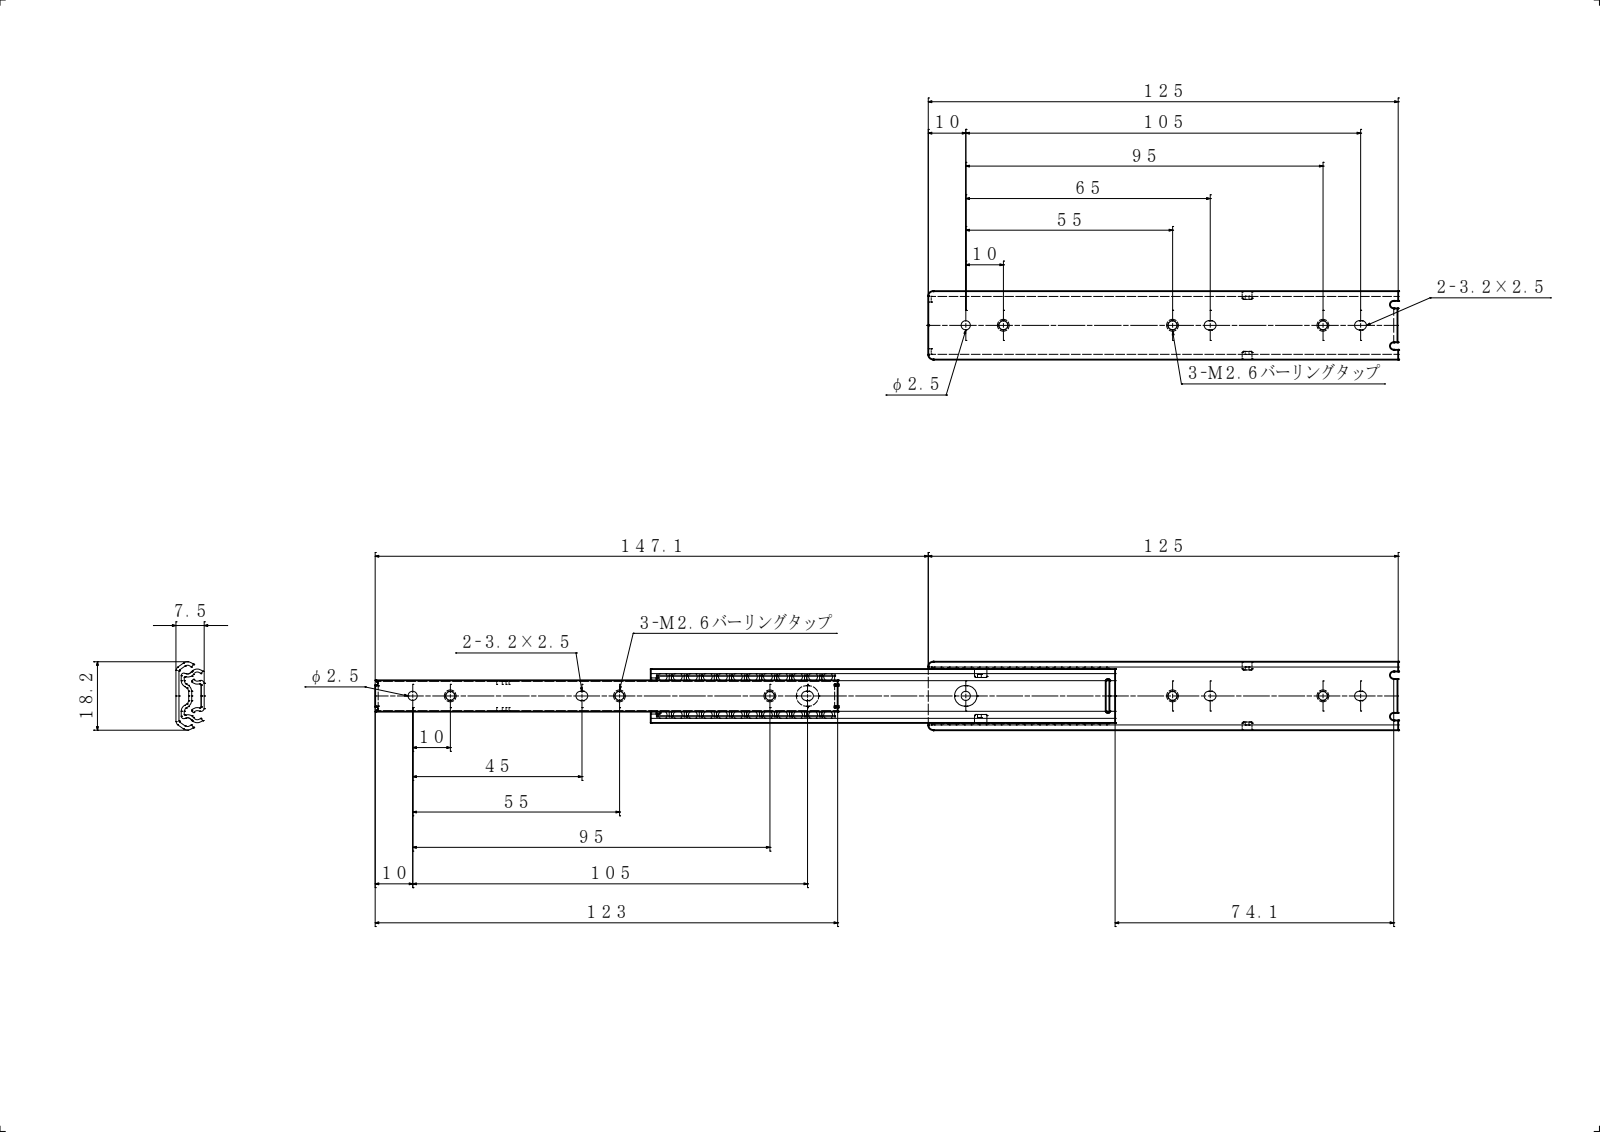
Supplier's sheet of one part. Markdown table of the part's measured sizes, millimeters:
| quantity | value |
| --- | --- |
| part name | UC180-125; UC180-125 IM; UC180-125 OM; UC180-125 CM |
| STEP written by | SolidWorks 2019 (CONFIG_CONTROL_DESIGN) |
| units | millimeters |
| bodies | 5 solids, 486 faces (198 planar, 234 cylindrical, 54 other) |
| overall size | 272.1 × 18.3 × 7.5 |
| volume | 6 056 mm³ |
| surface area | 16 079 mm² |
| round holes (diameter × count) | 2.2 × 3, 2.4 × 3, 2.5 × 2, 0.8 × 1 |
| round bosses / shafts (diameter × count) | 3.3 × 3, 3.2 × 3, 1.8 × 1 |
| partial cylindrical surfaces (radius × count) | 0.3 × 29, 1 × 14, 0.2 × 8, 0.5 × 8, 1.25 × 8, 1.8 × 8, 0.8 × 5, 0.1 × 4 |
| main face-to-face distances | 0.8, 6.7, 7.5, 5.9, 1.4, 5.3, 3.3, 2, 3.4, 0.6 |
| hole center spacings | 147.1, 10, 40, 45, 55, 85, 95, 2.6 |
